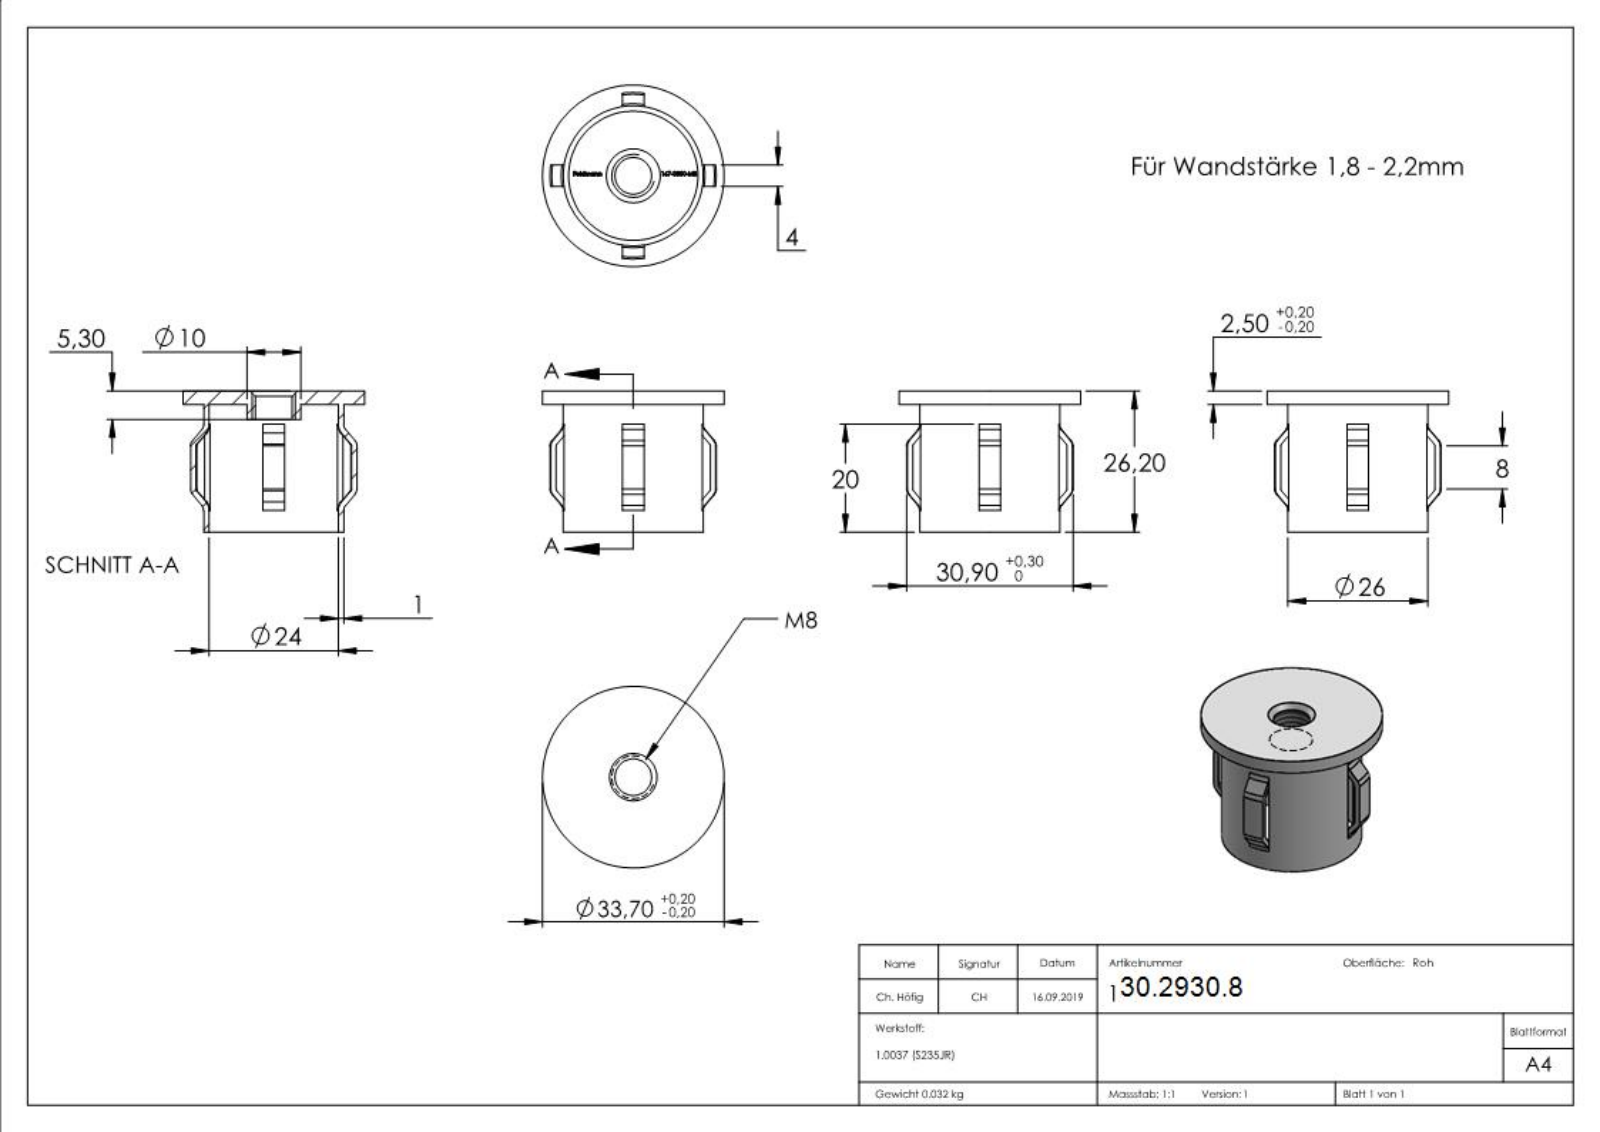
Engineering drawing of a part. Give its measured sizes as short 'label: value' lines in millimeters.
name: 167-3300-M8
written by: SolidWorks 2015 (CONFIG_CONTROL_DESIGN)
unit: mm
bodies: 1 solid, 346 faces (144 planar, 20 cylindrical, 182 other)
size: 33.7 × 33.7 × 26.2
volume: 4 132 mm³; area: 6 173 mm²
holes: 1× ⌀6.8, 1× ⌀24
bosses: 1× ⌀33.7, 1× ⌀26, 1× ⌀10
rounds: 1× R14.45, 1× R15.45
face distances: 2.5, 4, 23.7, 26.2, 20.9, 2.8, 5.3, 23.8, 2.9, 2.4
